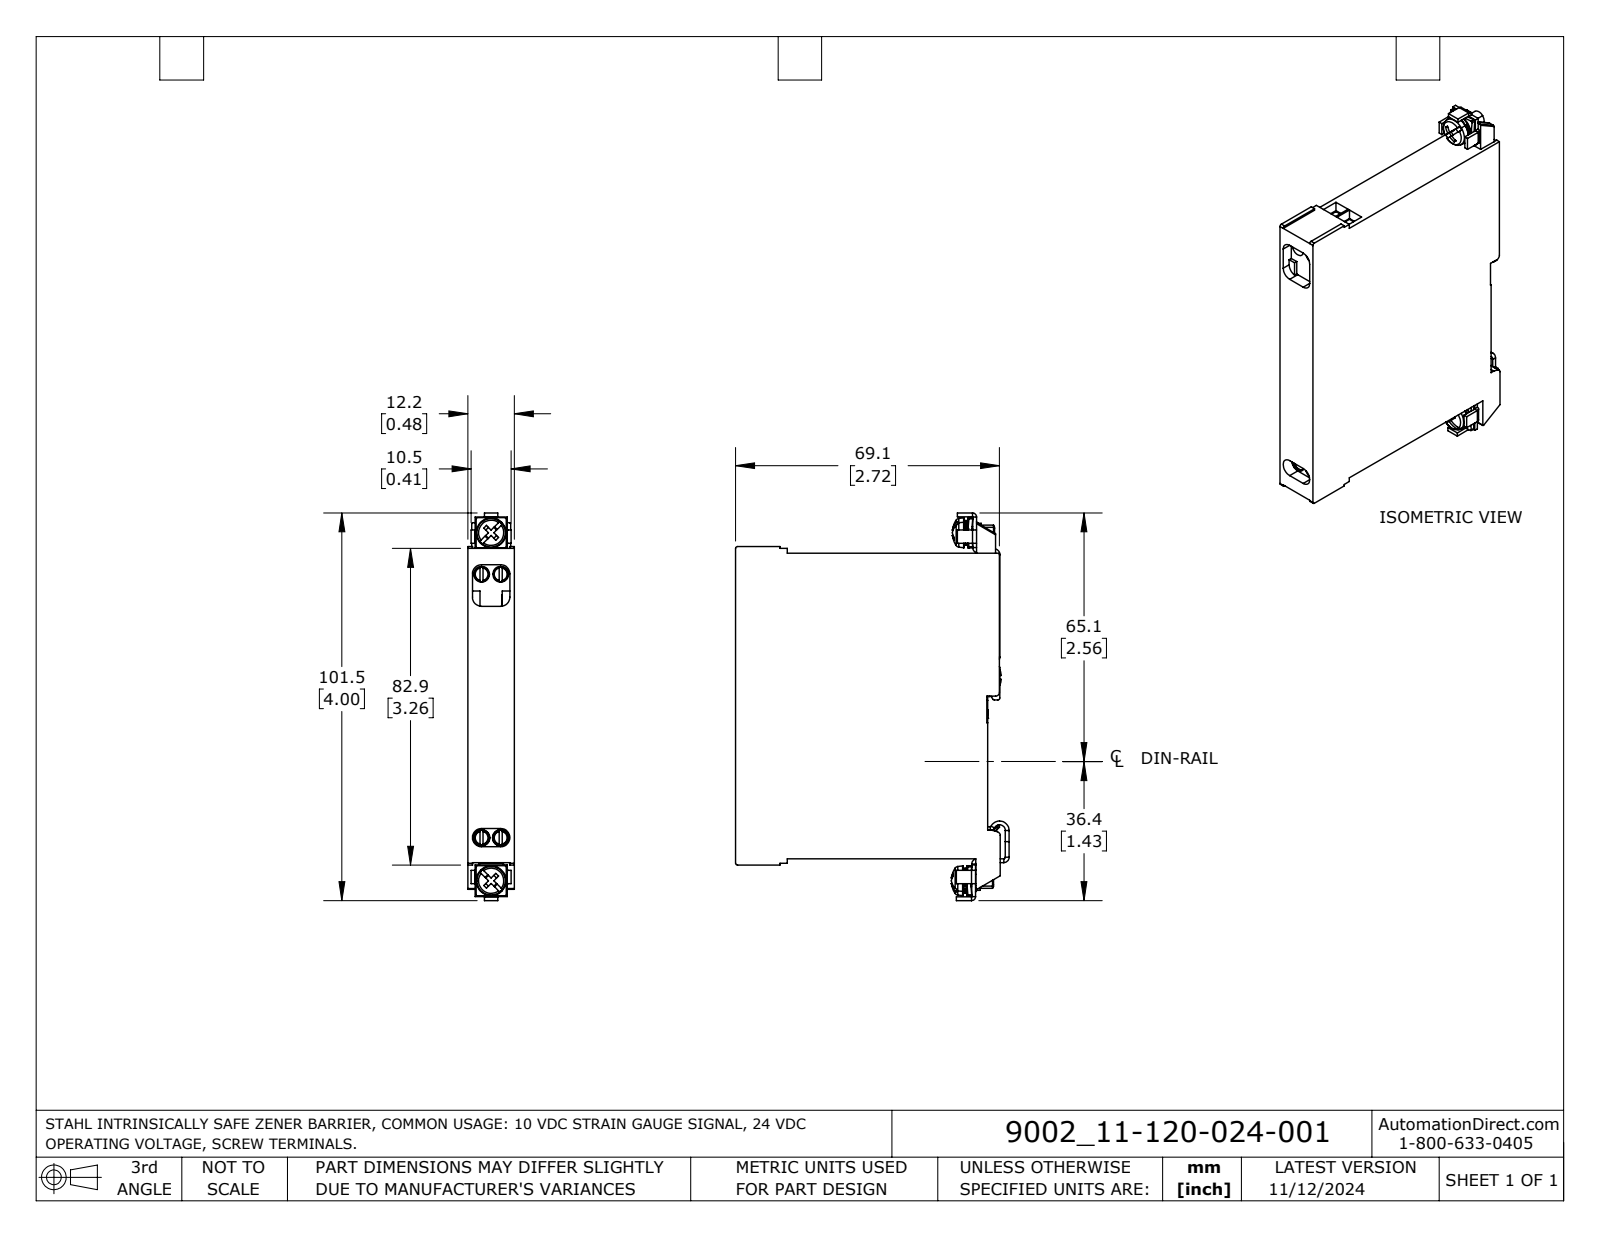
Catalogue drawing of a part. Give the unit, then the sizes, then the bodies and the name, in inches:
Units: inches
Overall size (bounding box): 3.996 × 2.82 × 0.48
Round holes (diameter × count): ⌀0.161 ×4, ⌀0.169 ×3, ⌀0.128 ×2, ⌀0.165 ×2, ⌀0.118 ×1
Round bosses / shafts (diameter × count): ⌀0.307 ×3, ⌀0.157 ×3, ⌀0.197 ×2, ⌀0.124 ×2, ⌀0.256 ×1
Partial cylindrical surfaces — rounded edges, fillets, slot ends (radius × count): R0.02 ×16, R0.012 ×8, R0.016 ×6, R0.039 ×6, R0.041 ×6, R0.055 ×6, R0.094 ×6, R0.01 ×4
Main face-to-face distances: 0.48, 0.039, 3.11, 0.043, 0.079, 3.071, 0.087, 3.15, 0.083, 0.047
Hole centre spacings: 0.197, 0.438, 0.454, 1.068, 1.111, 1.613, 1.656, 2.717
Volume: 3.982 in³ · Surface area: 33.72 in²
Bodies: 4 solids, 762 faces (528 planar, 146 cylindrical, 88 other)
Part name (STEP PRODUCT): 900211-120-024-001
STEP written by: SolidWorks 2023 (AUTOMOTIVE_DESIGN)
